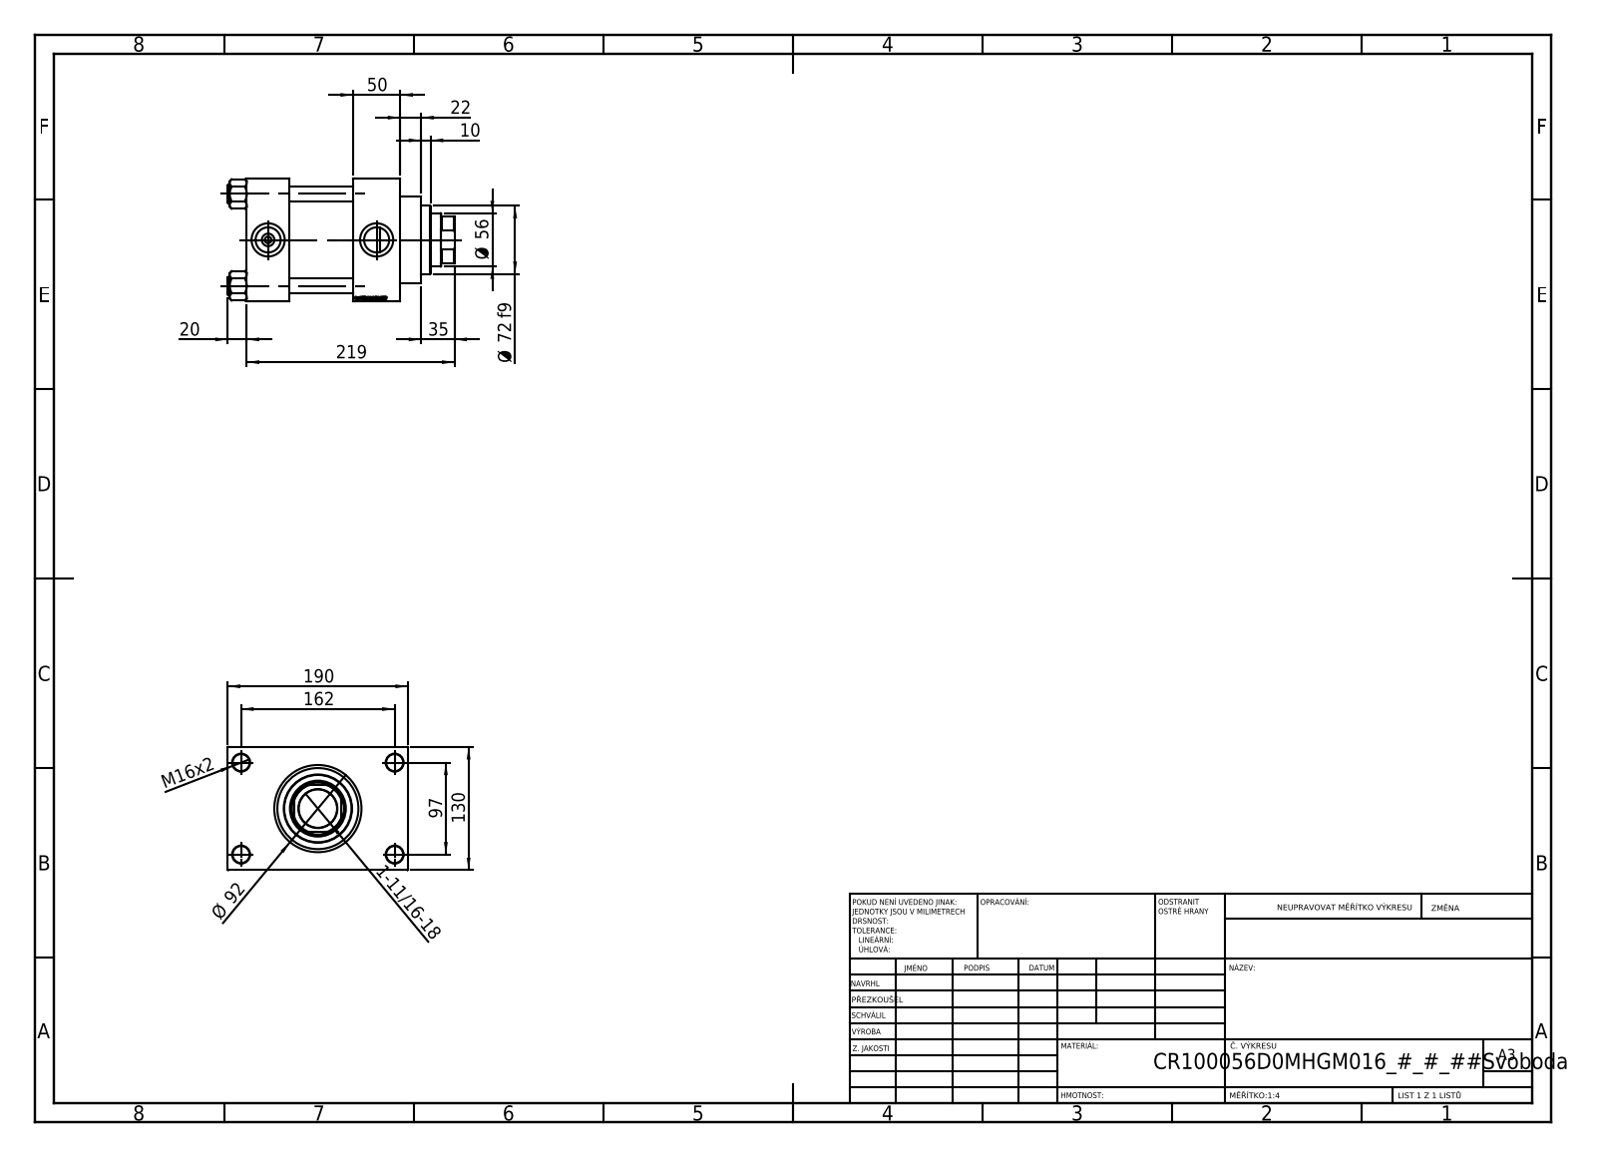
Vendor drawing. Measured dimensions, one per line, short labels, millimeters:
name: V215CR_D_Body; V215CR_VCP_D; V215CR_D_TYCINKA; NUT_M5_D (+1 more)
written by: SolidWorks 2019 (CONFIG_CONTROL_DESIGN)
unit: mm
bodies: 11 solids, 1151 faces (545 planar, 88 cylindrical, 518 other)
size: 239 × 190 × 130
volume: 2 611 000 mm³; area: 358 267 mm²
holes: 4× ⌀16, 4× ⌀18, 2× ⌀7, 2× ⌀26.44, 2× ⌀35, 1× ⌀40.5, 1× ⌀56, 1× ⌀59, 1× ⌀76, 1× ⌀85.5, 1× ⌀100
bosses: 4× ⌀19, 1× ⌀106, 1× ⌀92, 1× ⌀72
rounds: 1× R27
face distances: 130, 50, 45, 112, 67, 162, 117, 30, 160, 190
hole spacings: 32.55, 68.52, 94.41, 96.9, 102.27, 129.45, 161.73, 97
